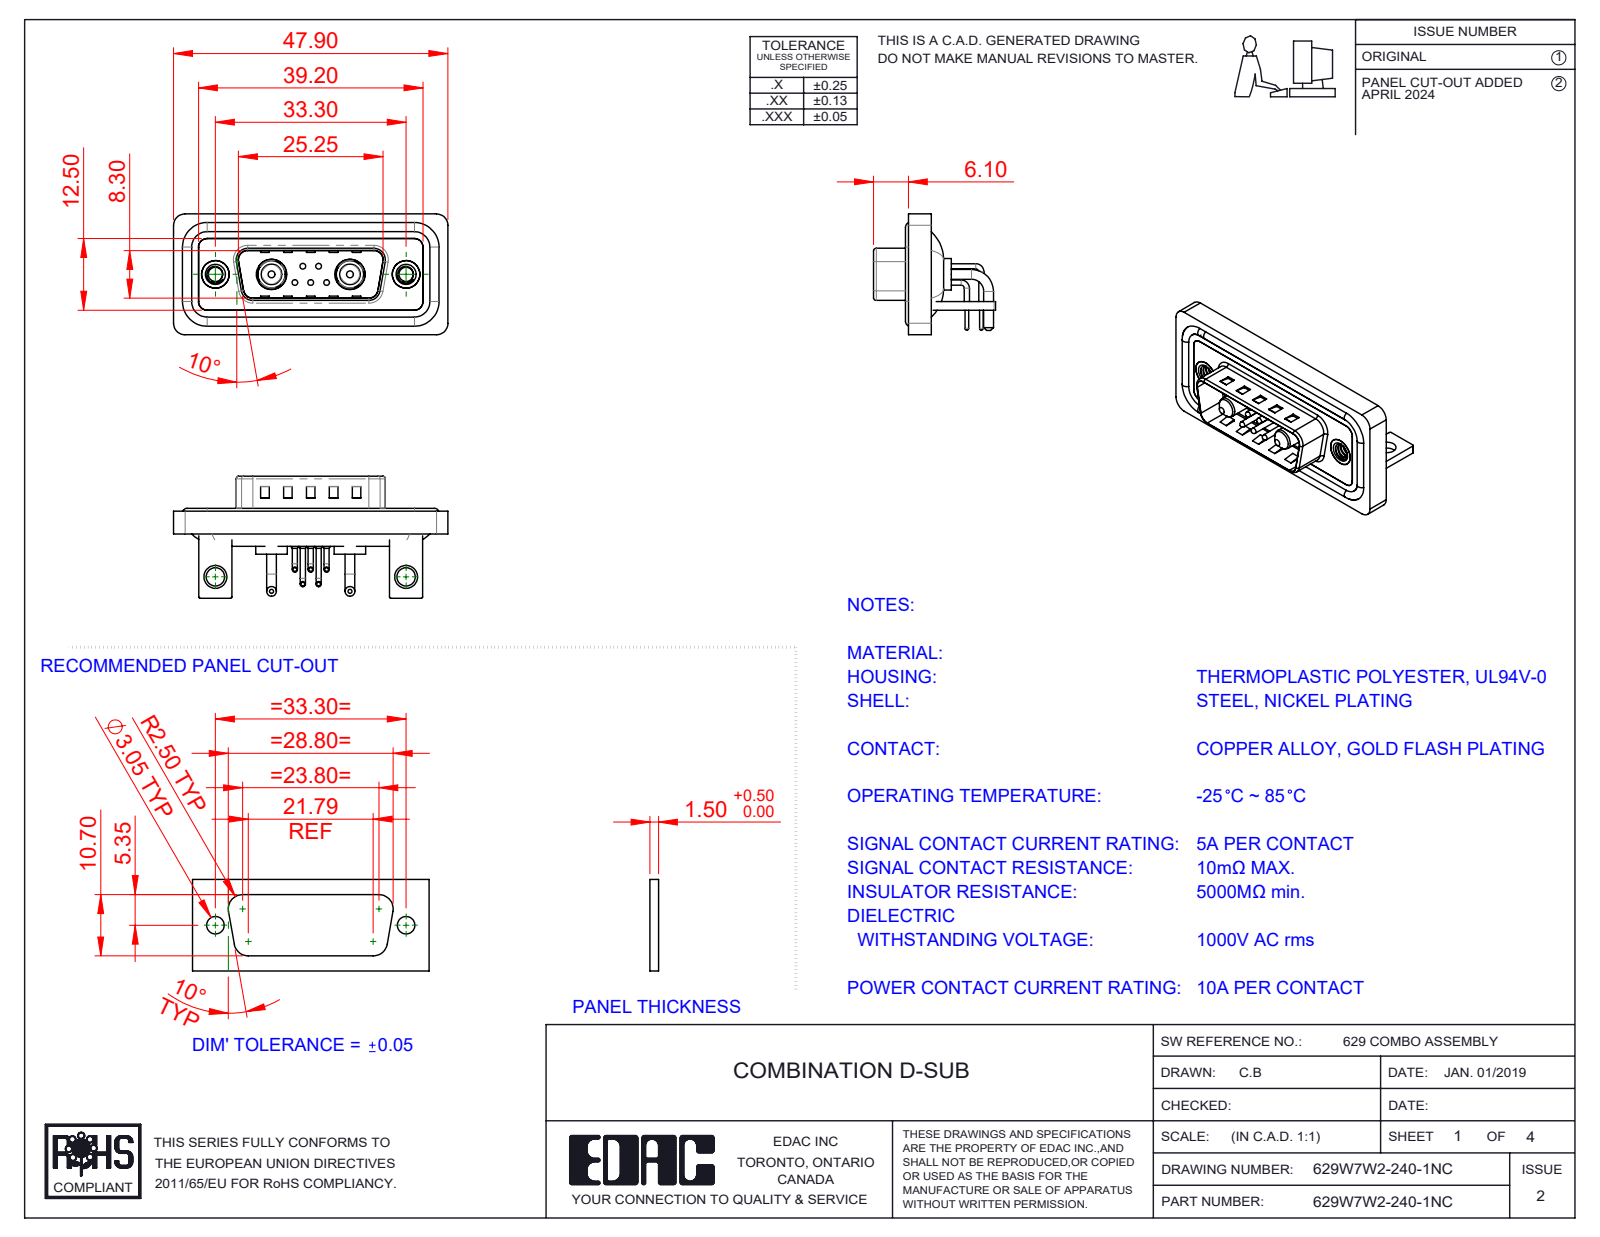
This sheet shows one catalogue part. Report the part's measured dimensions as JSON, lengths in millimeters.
{"part_name": "629Combo Stabilizer Bracket; 629Combo Housing_7W2; 629Combo Shell Front_15 Contacts; 629Combo Contact Row 1 (+6 more)", "step_written_by": "SolidWorks 2023 (CONFIG_CONTROL_DESIGN)", "units": "millimeters", "bodies": {"solids": 18, "faces": 1121, "planar": 537, "cylindrical": 424, "other": 160}, "overall_size": [47.9, 21.3, 21.1], "volume_mm3": 5836, "surface_area_mm2": 9627, "round_holes": [[0.75, 5], [1.6, 5], [2, 5], [2.5, 2], [3.2, 2], [4, 2], [4.8, 2], [4.85, 2], [5, 2], [5.3, 2]], "round_bosses_or_shafts": [[0.9, 10], [1.5, 5], [1, 5], [0.65, 5], [1.7, 4], [1.6, 4], [5.5, 2], [5.2, 2]], "partial_cylinders_radius": [[2, 21], [1.5, 18], [0.25, 16], [0.5, 9], [1.6, 8], [1.01, 5], [0.6, 4], [0.65, 4]], "face_to_face_distances": [0.4, 1.5, 0.8, 2.9, 2.1, 1.1, 1.6, 1.2, 3.7, 4.5], "hole_center_spacings": [3.16, 2.77, 9.8, 23.5, 33.3, 4.31, 4.33, 5.03]}
